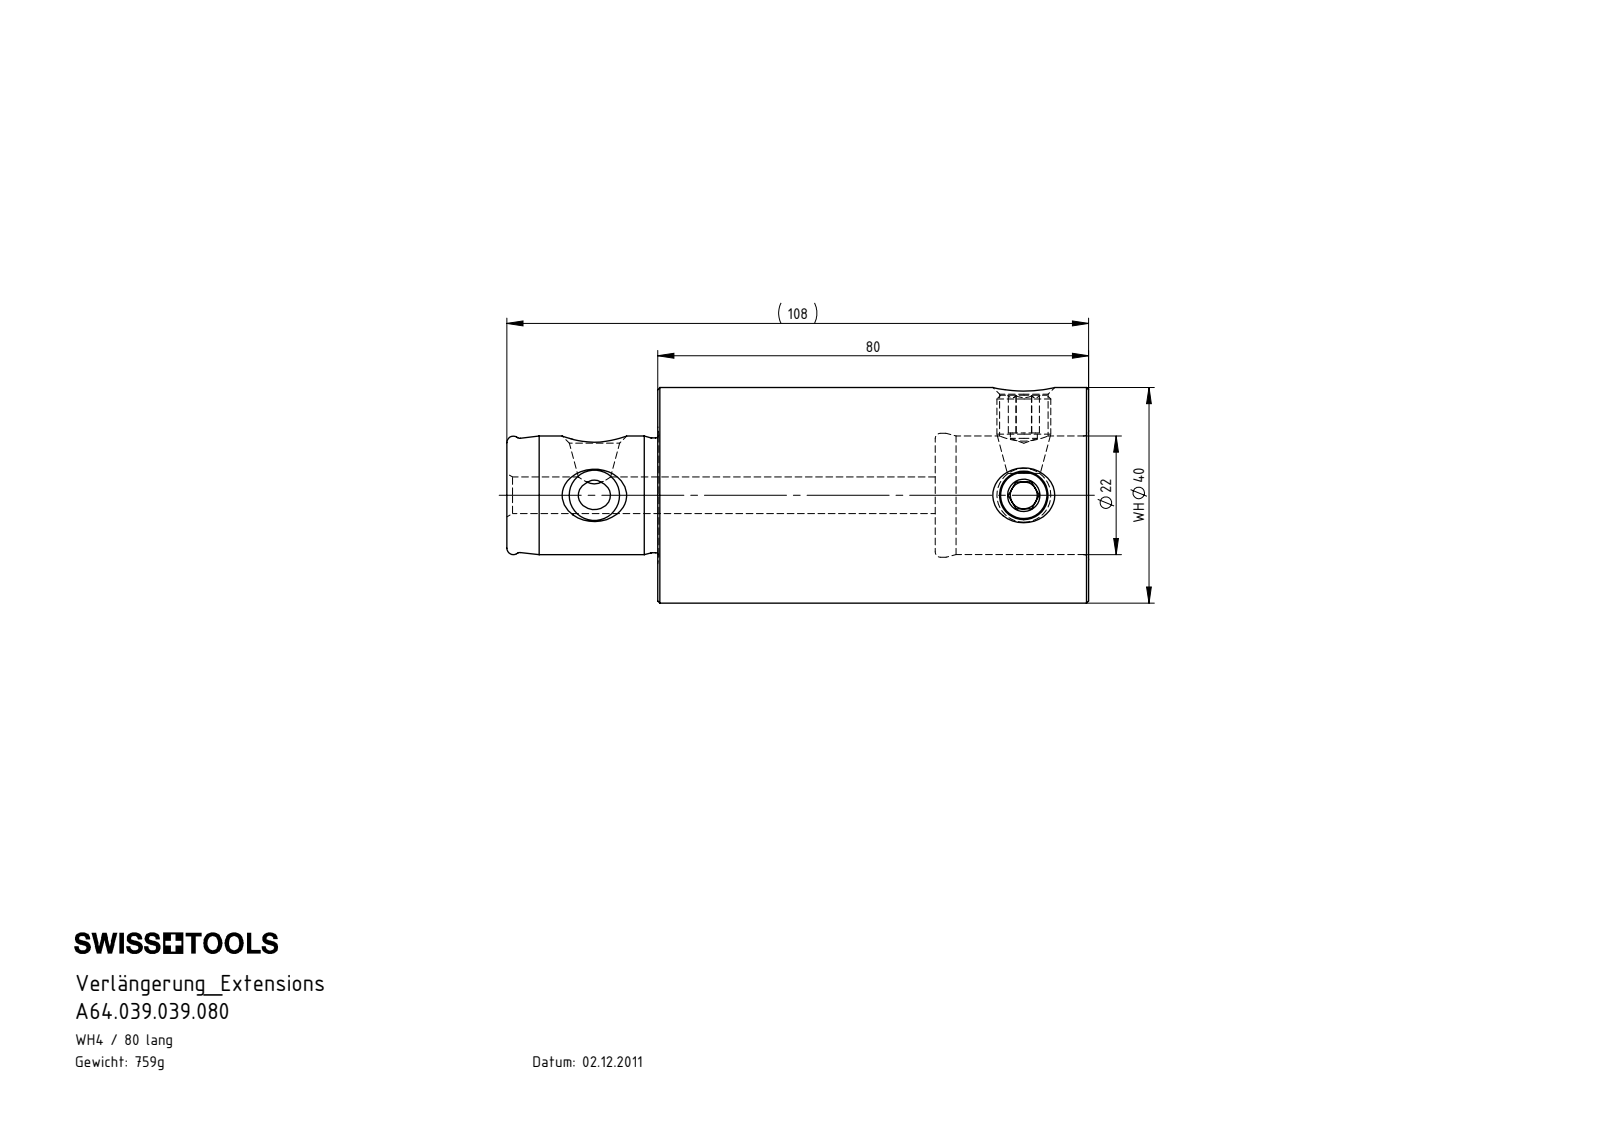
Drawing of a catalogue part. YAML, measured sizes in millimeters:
part_name: "WH4-ER1.001.015; WH4-WH4.001.080; WH4-WH4.001.080_A"
step_written_by: "SolidWorks 2015 (AUTOMOTIVE_DESIGN)"
units: millimeters
bodies: {solids: 3, faces: 94, planar: 22, cylindrical: 20, other: 52}
overall_size: [108, 39, 39]
volume: 92009
surface_area: 19219
round_holes:
  - {diameter: 9, count: 2}
  - {diameter: 6.8, count: 1}
  - {diameter: 22, count: 1}
  - {diameter: 23, count: 1}
round_bosses_or_shafts:
  - {diameter: 10, count: 2}
  - {diameter: 39, count: 1}
  - {diameter: 21.3, count: 1}
face_to_face_distances: [80, 51.5, 28.5, 28, 79.5, 108, 5, 14.5, 9.5]
